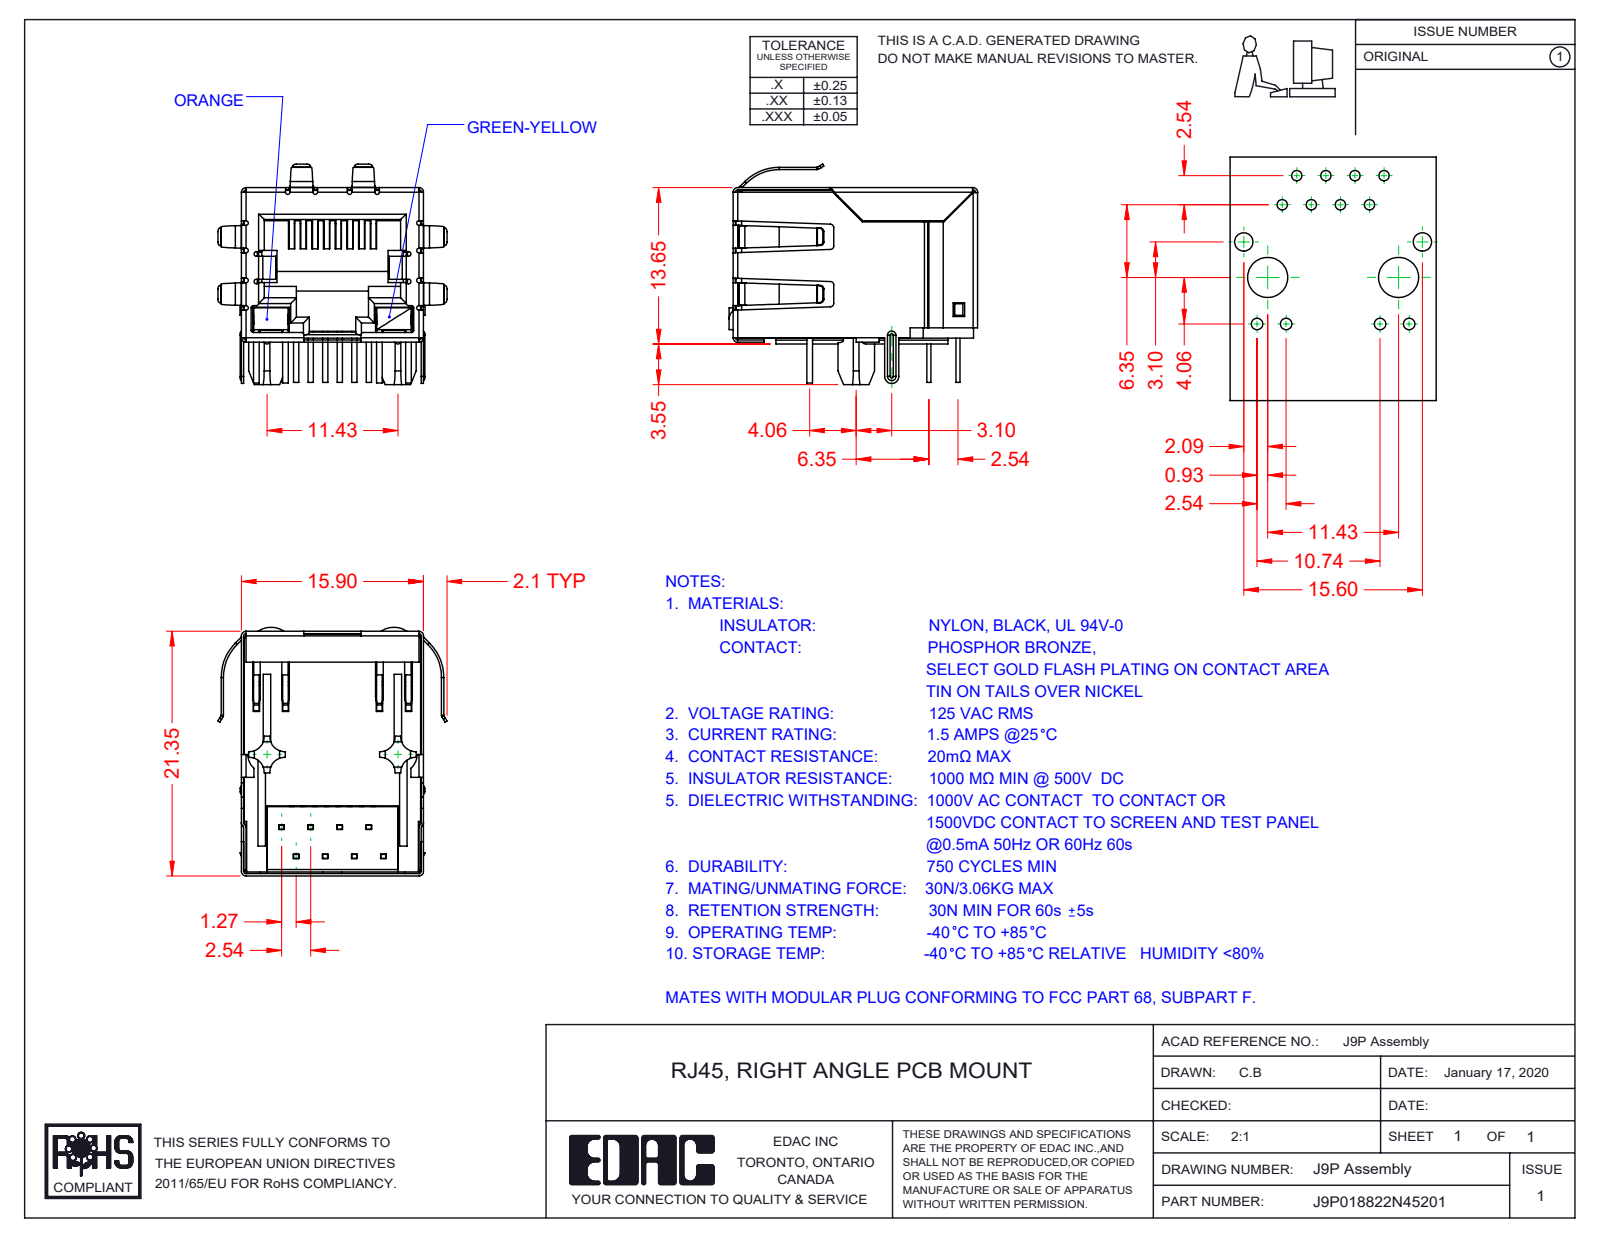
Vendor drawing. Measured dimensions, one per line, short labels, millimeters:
name: 9P-LED Assembly; 9P-LED LED RH_5-Green-Yellow; 9P-LED LED LH_4-Orange; 9P-LED Contact Lock (+4 more)
written by: SolidWorks 2016 (CONFIG_CONTROL_DESIGN)
unit: mm
bodies: 13 solids, 1474 faces (1042 planar, 338 cylindrical, 94 other)
size: 21.7 × 20 × 19.25
volume: 2 687 mm³; area: 7 515 mm²
rounds: 39× R0.2, 22× R0.5, 20× R0.3, 16× R0.4, 8× R1.3, 5× R0.23, 4× R0.11, 4× R0.31
face distances: 15.45, 15.7, 15.65, 0.35, 0.54, 15.5, 12.36, 0.6, 1.4, 0.59
